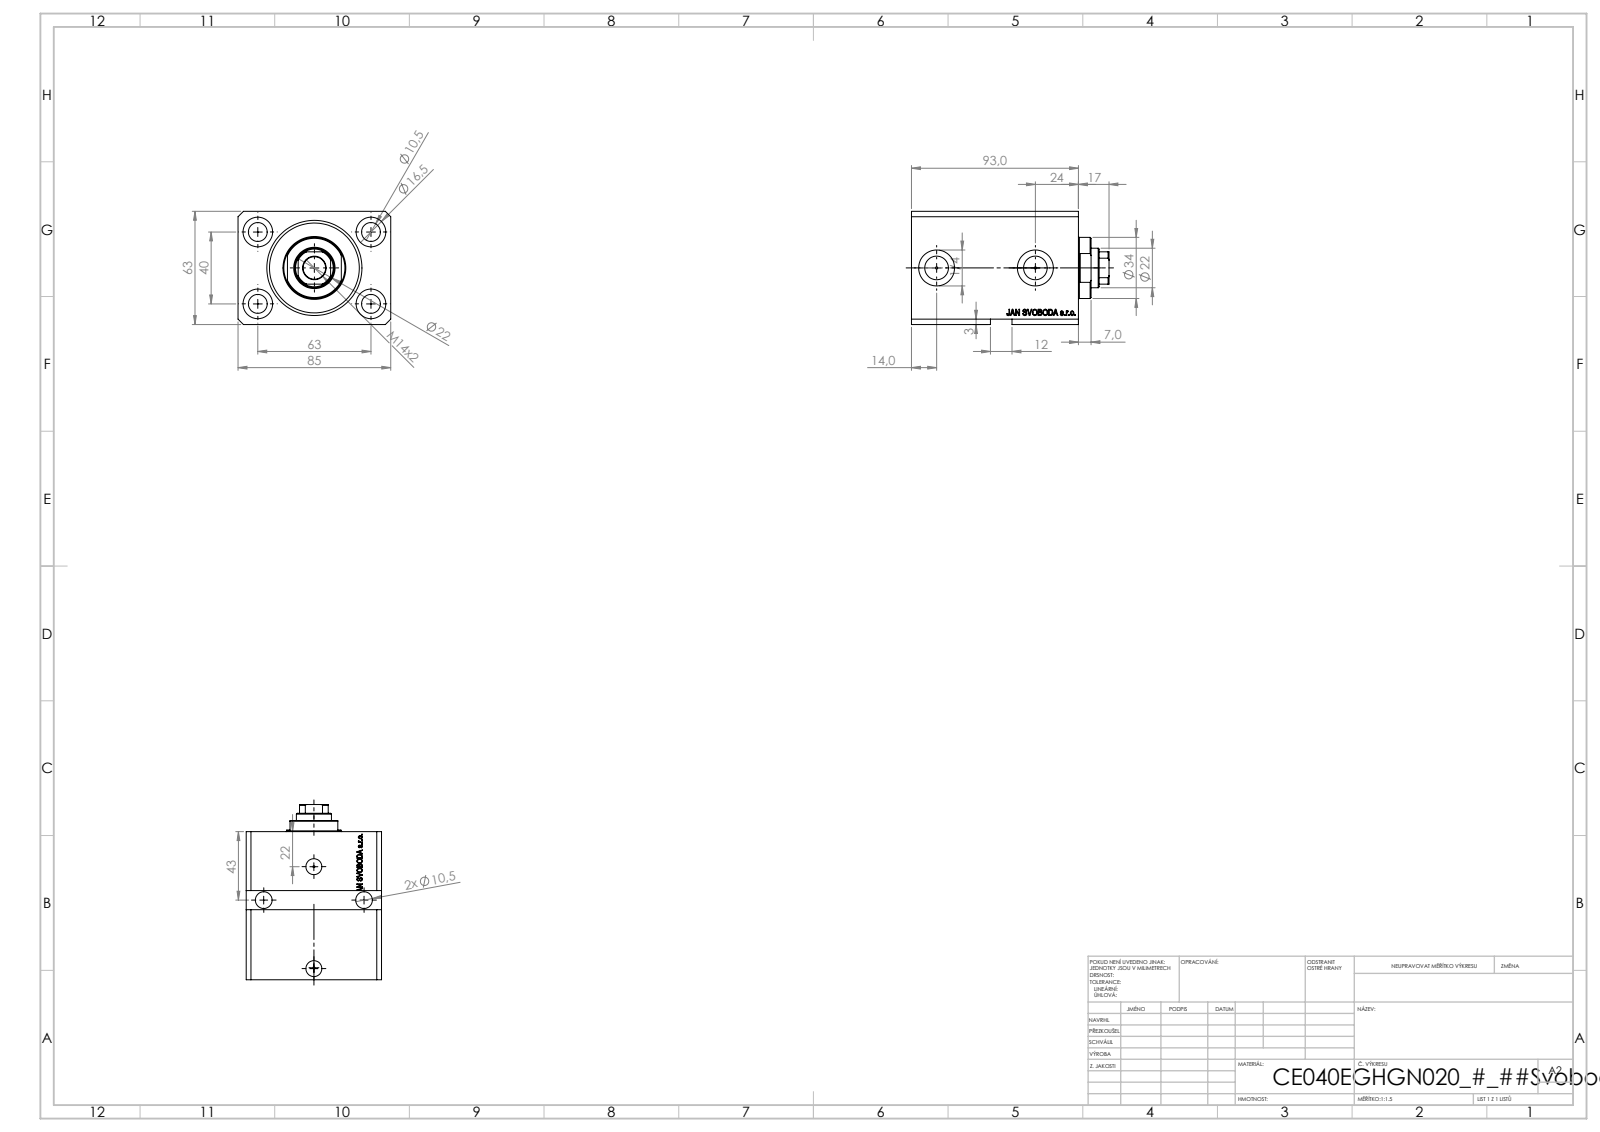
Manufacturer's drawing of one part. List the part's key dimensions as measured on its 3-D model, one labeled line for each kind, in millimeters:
Part name (STEP PRODUCT): V250CE_C_VCP; V250CE_E_Body; V250CE_VC_E
STEP written by: SolidWorks 2019 (CONFIG_CONTROL_DESIGN)
Units: millimetres
Bodies: 3 solids, 917 faces (459 planar, 84 cylindrical, 374 other)
Overall size (bounding box): 110 × 85 × 63
Volume: 427 173 mm³ · Surface area: 87 247 mm²
Round holes (diameter × count): ⌀10.5 ×6, ⌀1.25 ×4, ⌀16.5 ×4, ⌀10 ×2, ⌀13.16 ×2, ⌀20 ×2, ⌀12.5 ×1, ⌀22 ×1, ⌀40 ×1, ⌀53 ×1
Round bosses / shafts (diameter × count): ⌀34 ×1
Partial cylindrical surfaces — rounded edges, fillets, slot ends (radius × count): R10.5 ×1
Main face-to-face distances: 63, 85, 93, 17, 76, 11.4, 64.6, 81.6, 56, 44.6
Hole centre spacings: 37.31, 63, 37.86, 40, 52.88, 53.3, 74.63, 0.53
